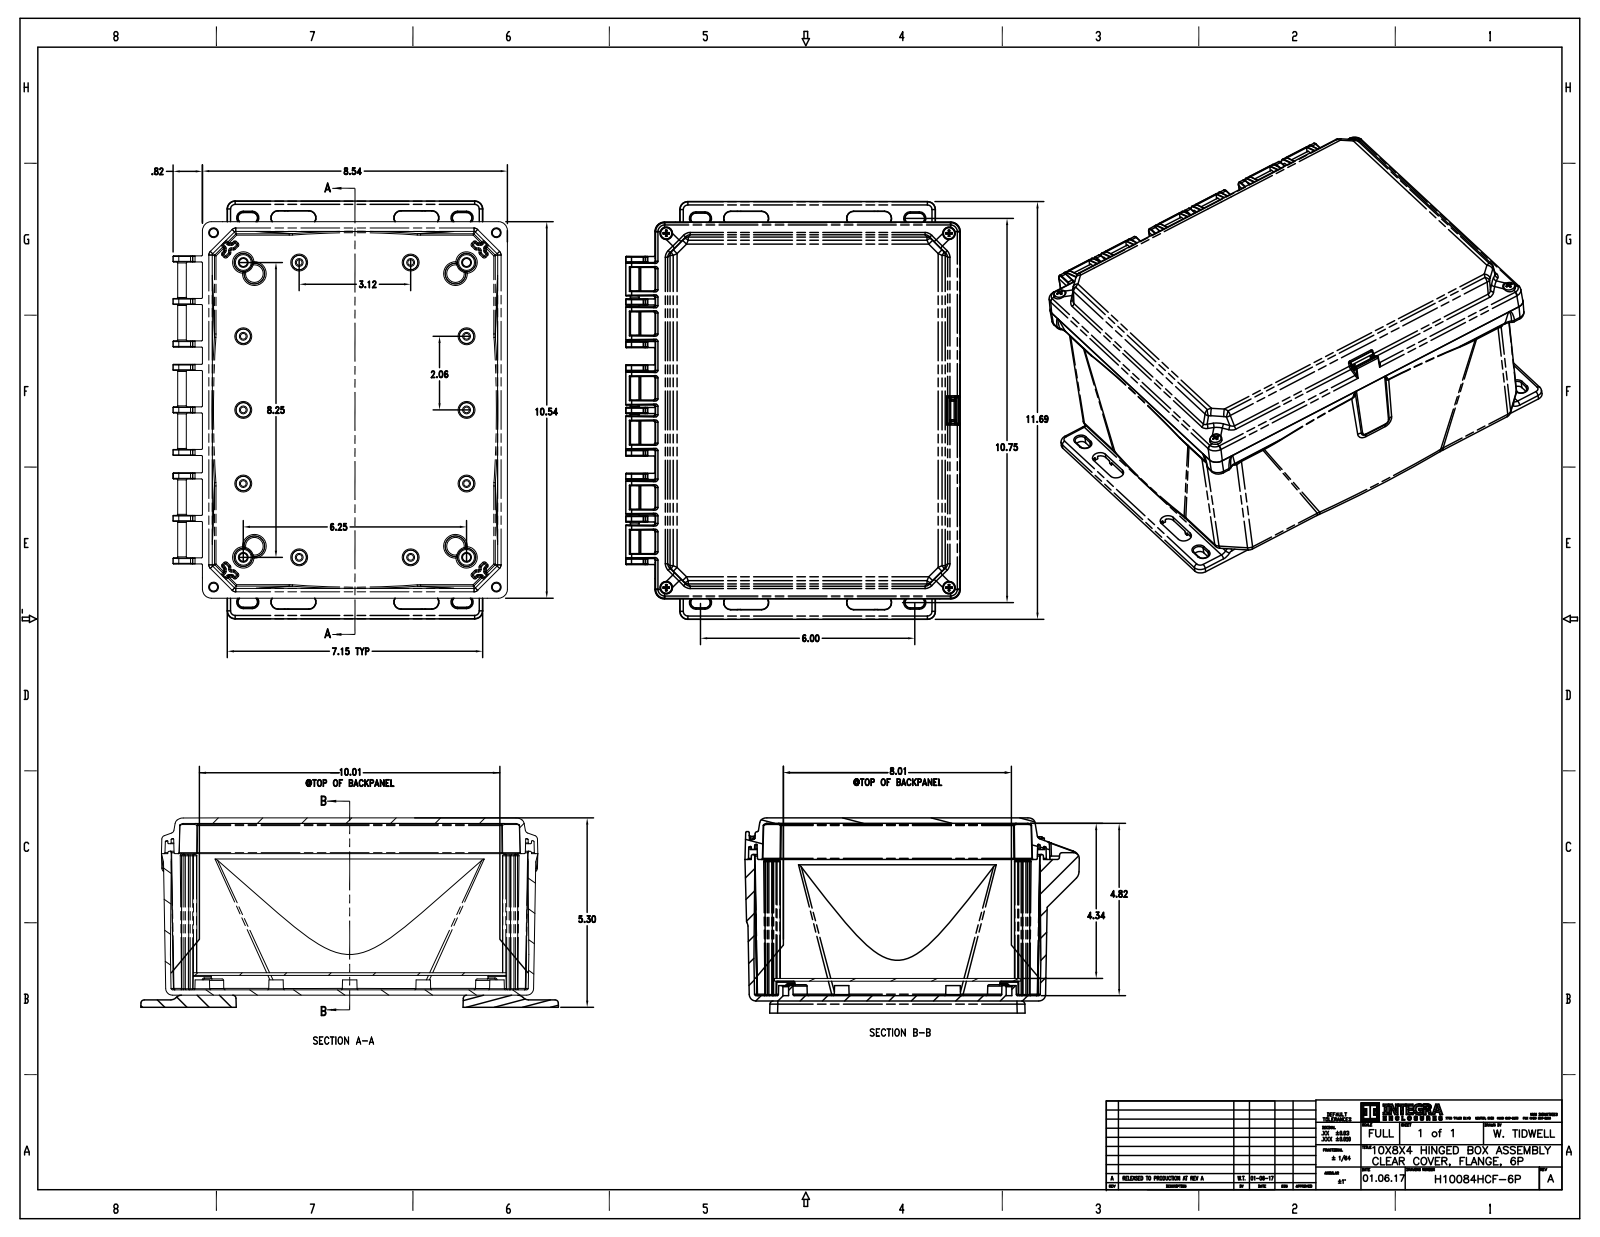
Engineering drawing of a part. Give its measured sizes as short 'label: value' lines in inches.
name: H1084BH; 9912525-80-10; 9912521-80-10; H1084BH_ASM (+5 more)
written by: CREO PARAMETRIC BY PTC INC, 2016050 (CONFIG_CONTROL_DESIGN)
unit: in
bodies: 24 solids, 4309 faces (1060 planar, 1765 cylindrical, 1484 other)
size: 11.69 × 9.359 × 5.465
volume: 65.87 in³; area: 909.4 in²
holes: 10× ⌀0.16, 8× ⌀0.19, 4× ⌀0.201
bosses: 12× ⌀0.25, 8× ⌀0.3, 8× ⌀0.298, 8× ⌀0.29, 8× ⌀0.26, 8× ⌀0.258, 4× ⌀0.375, 4× ⌀0.372
rounds: 340× R0.03, 169× R0.02, 90× R0.015, 49× R0.005, 43× R0.01, 38× R0.09, 36× R0.04, 28× R0.1
face distances: 0.15, 0.49, 0.12, 3.81, 3.96, 0.392, 0.27, 4.08, 0.34, 0.098
hole spacings: 9.916, 6.25, 0.439, 1.178, 1.293, 1.565, 1.616, 1.782
